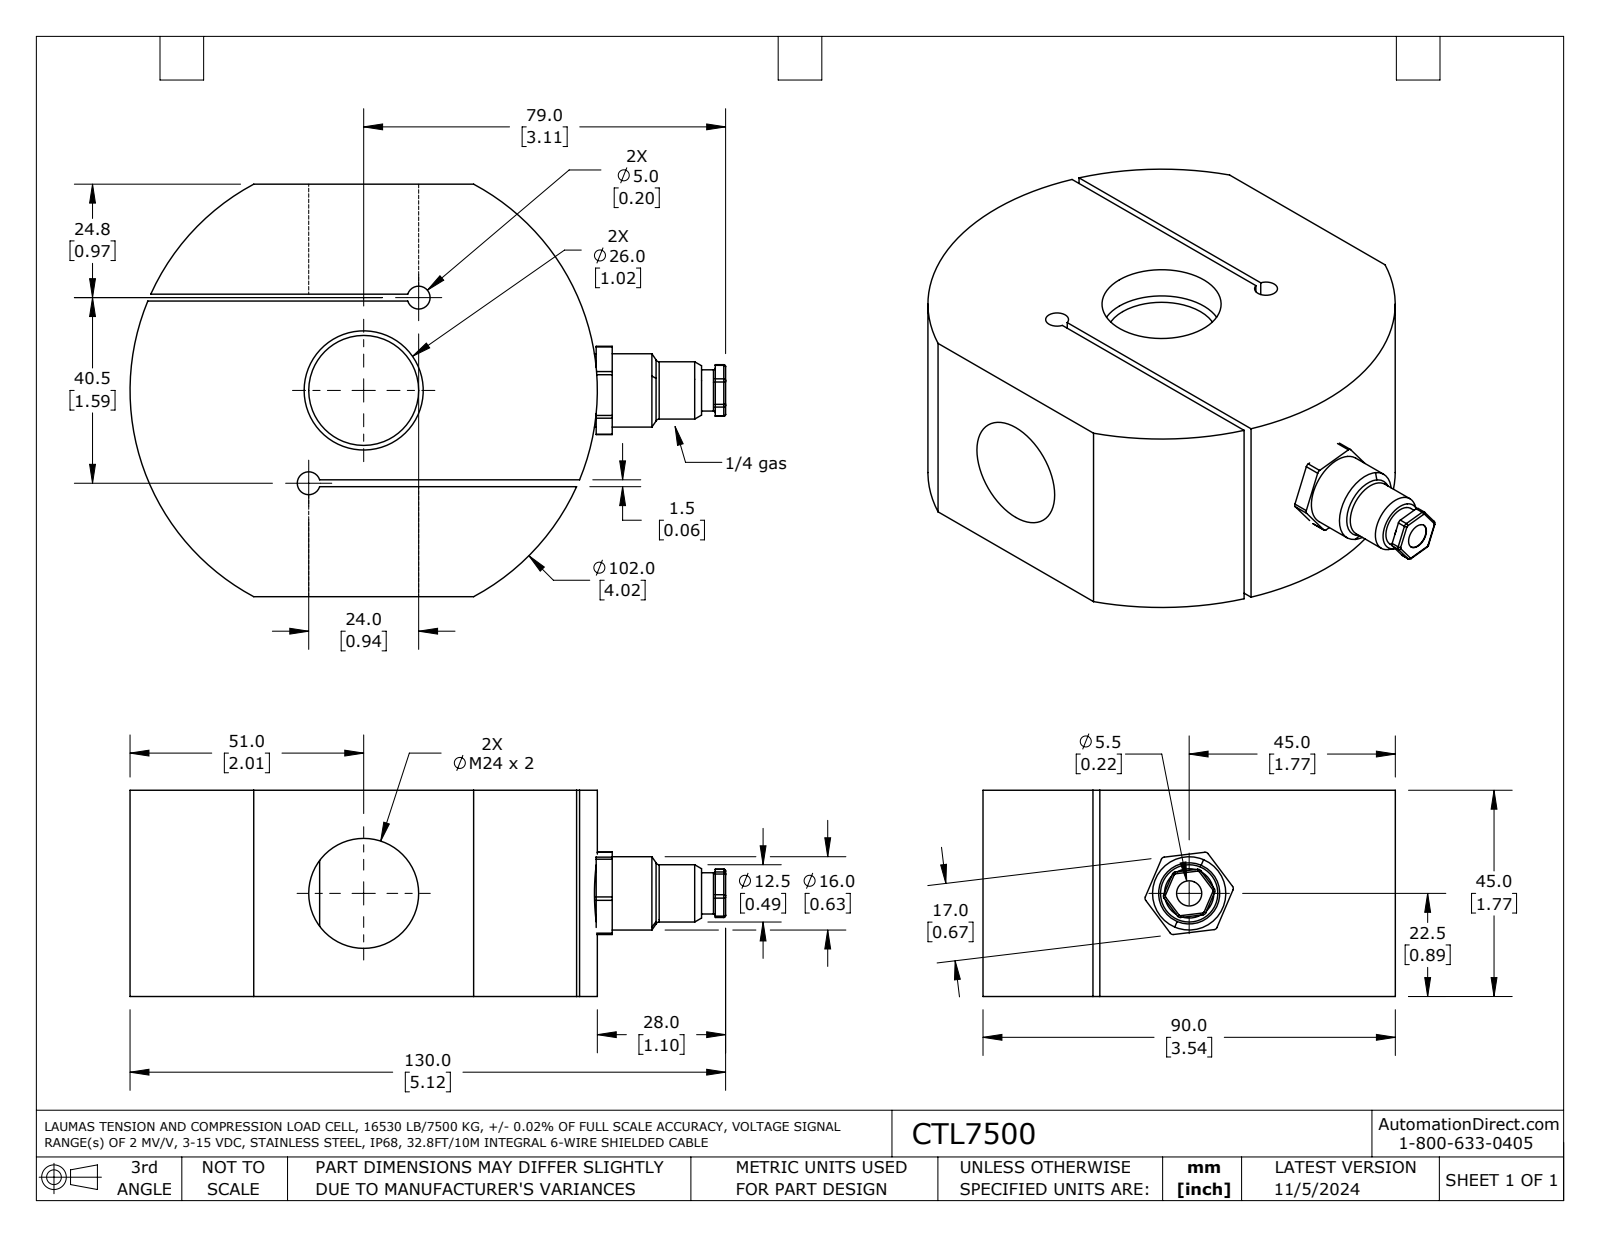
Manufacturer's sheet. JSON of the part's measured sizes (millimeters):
{"part_name": "CTL7500", "step_written_by": "SolidWorks 2021 (AUTOMOTIVE_DESIGN)", "units": "millimeters", "bodies": {"solids": 2, "faces": 100, "planar": 31, "cylindrical": 50, "other": 19}, "overall_size": [130, 90, 45], "volume_mm3": 313200, "surface_area_mm2": 45930, "round_holes": [[5, 2], [5.5, 1], [14, 1], [24, 1], [26, 1]], "round_bosses_or_shafts": [[16, 1], [12.5, 1], [9, 1]], "partial_cylinders_radius": [[0.8, 12], [0.4, 6], [51, 1]], "face_to_face_distances": [45, 1.5, 40.5, 24, 25.5, 64.5, 66, 39, 42, 90], "hole_center_spacings": [23.5, 47.1]}
